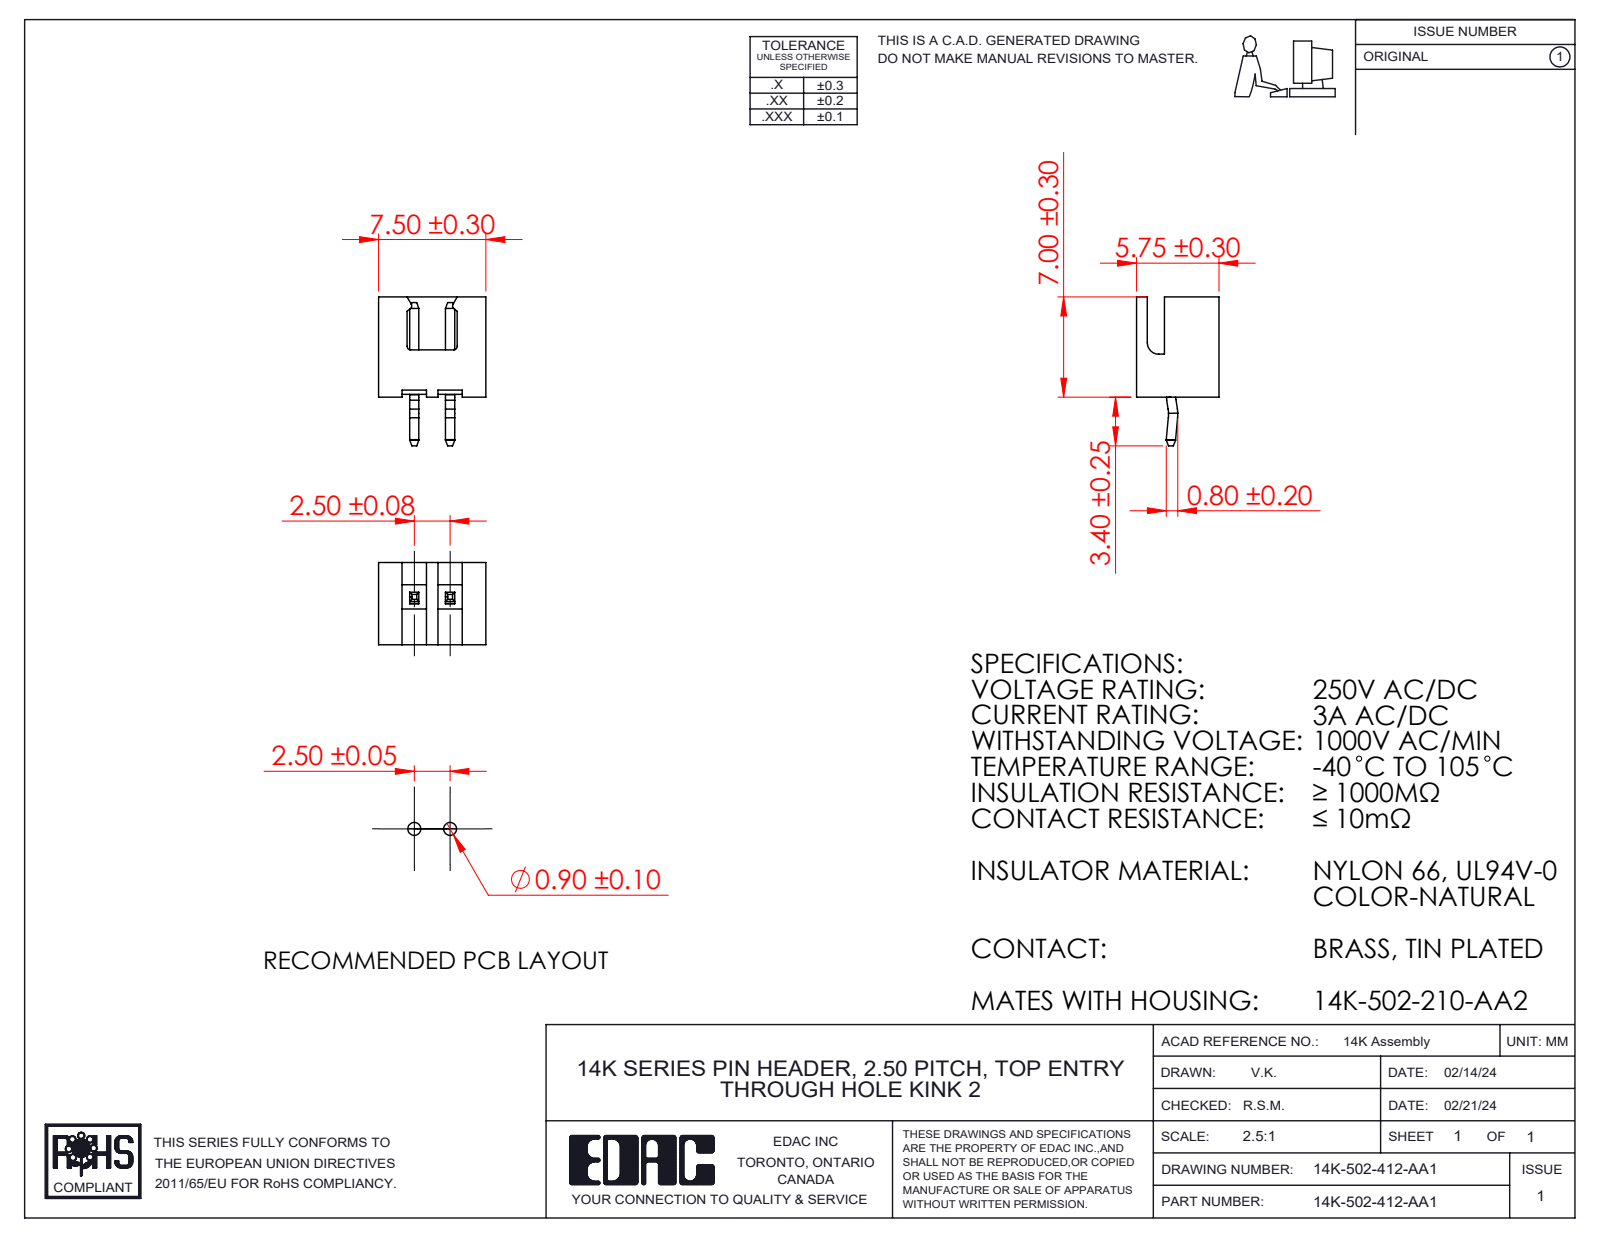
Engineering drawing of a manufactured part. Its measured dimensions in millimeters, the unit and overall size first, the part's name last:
Units: millimetres
Overall size (bounding box): 10.4 × 7.5 × 5.75
Partial cylindrical surfaces — rounded edges, fillets, slot ends (radius × count): R0.25 ×4, R2.5 ×4, R0.8 ×1
Main face-to-face distances: 0.76, 5, 5.76, 7.5, 0.75, 6.75, 0.64, 4.24, 2.5, 1.95
Volume: 152 mm³ · Surface area: 415 mm²
Bodies: 3 solids, 122 faces (103 planar, 19 cylindrical, 0 other)
Part name (STEP PRODUCT): 14K Series Pin Header Insulator_502; 14K Series Pin_12; 14K-502-412-AA1
STEP written by: SolidWorks 2023 (CONFIG_CONTROL_DESIGN)
